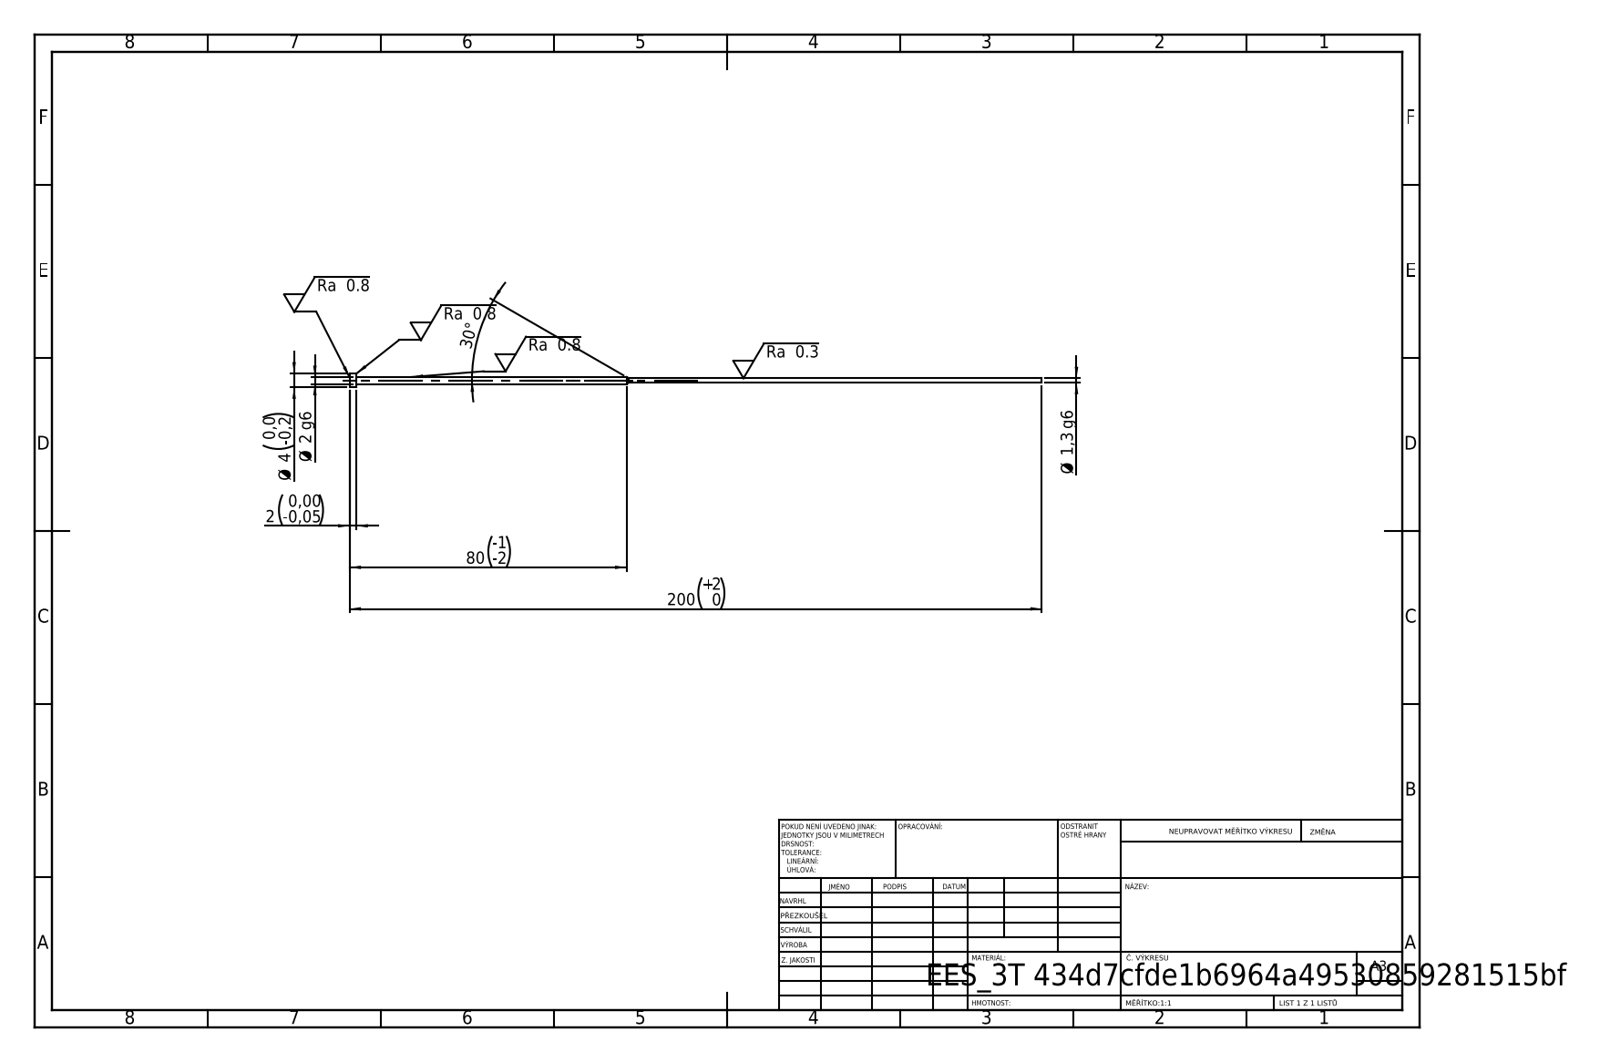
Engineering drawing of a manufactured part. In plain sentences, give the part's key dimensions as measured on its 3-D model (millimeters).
Its 3-D file was written by "SolidWorks 2019 (CONFIG_CONTROL_DESIGN)". It is 1 solid with 11 faces: 3 planar, 6 cylindrical and 2 other. Overall it measures 200 by 4 by 4 millimeters. Its volume is 430 cubic millimeters and its surface area 1 030 square millimeters. Round bosses or shafts: 1 of diameter 4, 1 of diameter 2, 1 of diameter 1.3. The main face-to-face distances are 2, 198, 200.
